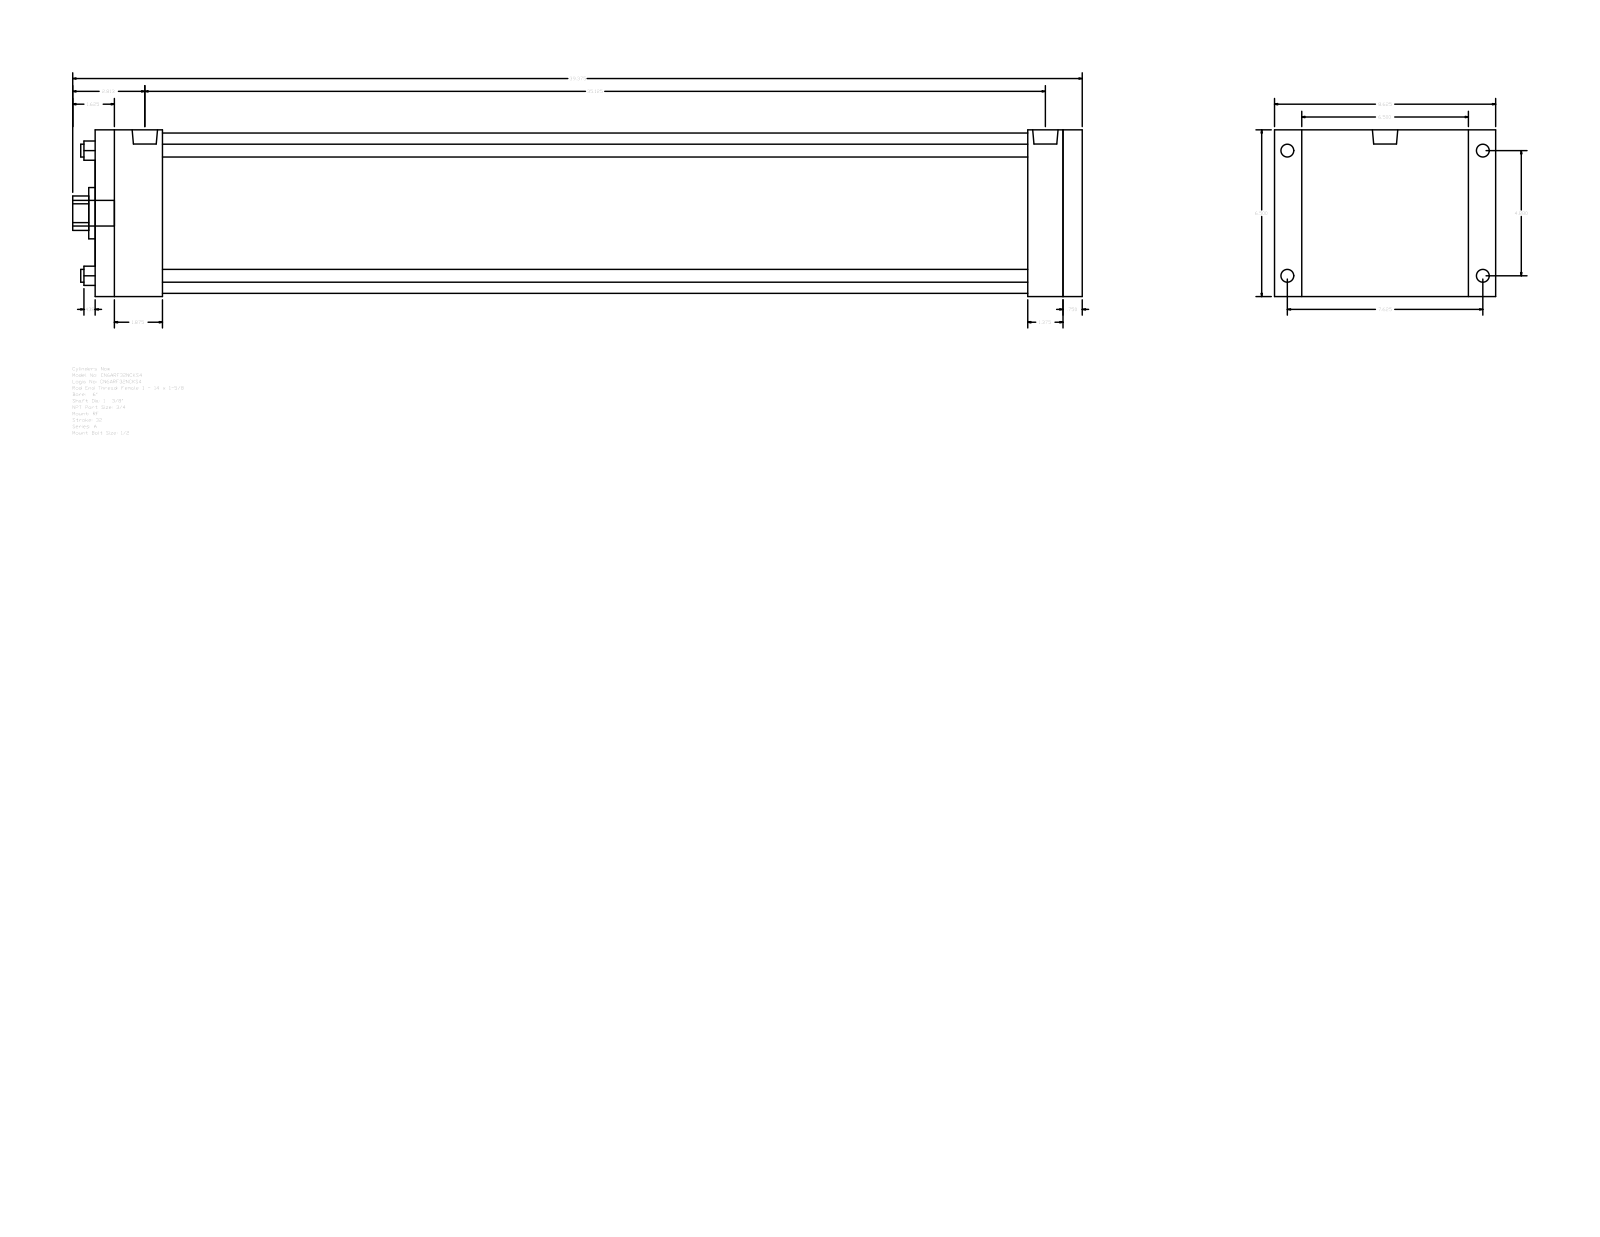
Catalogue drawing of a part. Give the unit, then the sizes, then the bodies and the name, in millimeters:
Units: millimetres
Overall size (bounding box): 1000.12 × 219.07 × 165.1
Round holes (diameter × count): ⌀12.7 ×4, ⌀34.92 ×1, ⌀50.8 ×1, ⌀158.75 ×1
Round bosses / shafts (diameter × count): ⌀15.08 ×4, ⌀12.7 ×4, ⌀25.12 ×2, ⌀25.4 ×1
Partial cylindrical surfaces — rounded edges, fillets, slot ends (radius × count): R17.06 ×1
Main face-to-face distances: 165.1, 977.89, 19.04, 958.85, 66.67, 892.18, 911.22, 923.92, 857.25, 34.93
Hole centre spacings: 87.65, 123.96, 175.31
Bodies: 0 solids, 92 faces (64 planar, 28 cylindrical, 0 other)
Part name (STEP PRODUCT): A_RF__0600_1.375
STEP written by: GSSL Pune (CONFIG_CONTROL_DESIGN)
